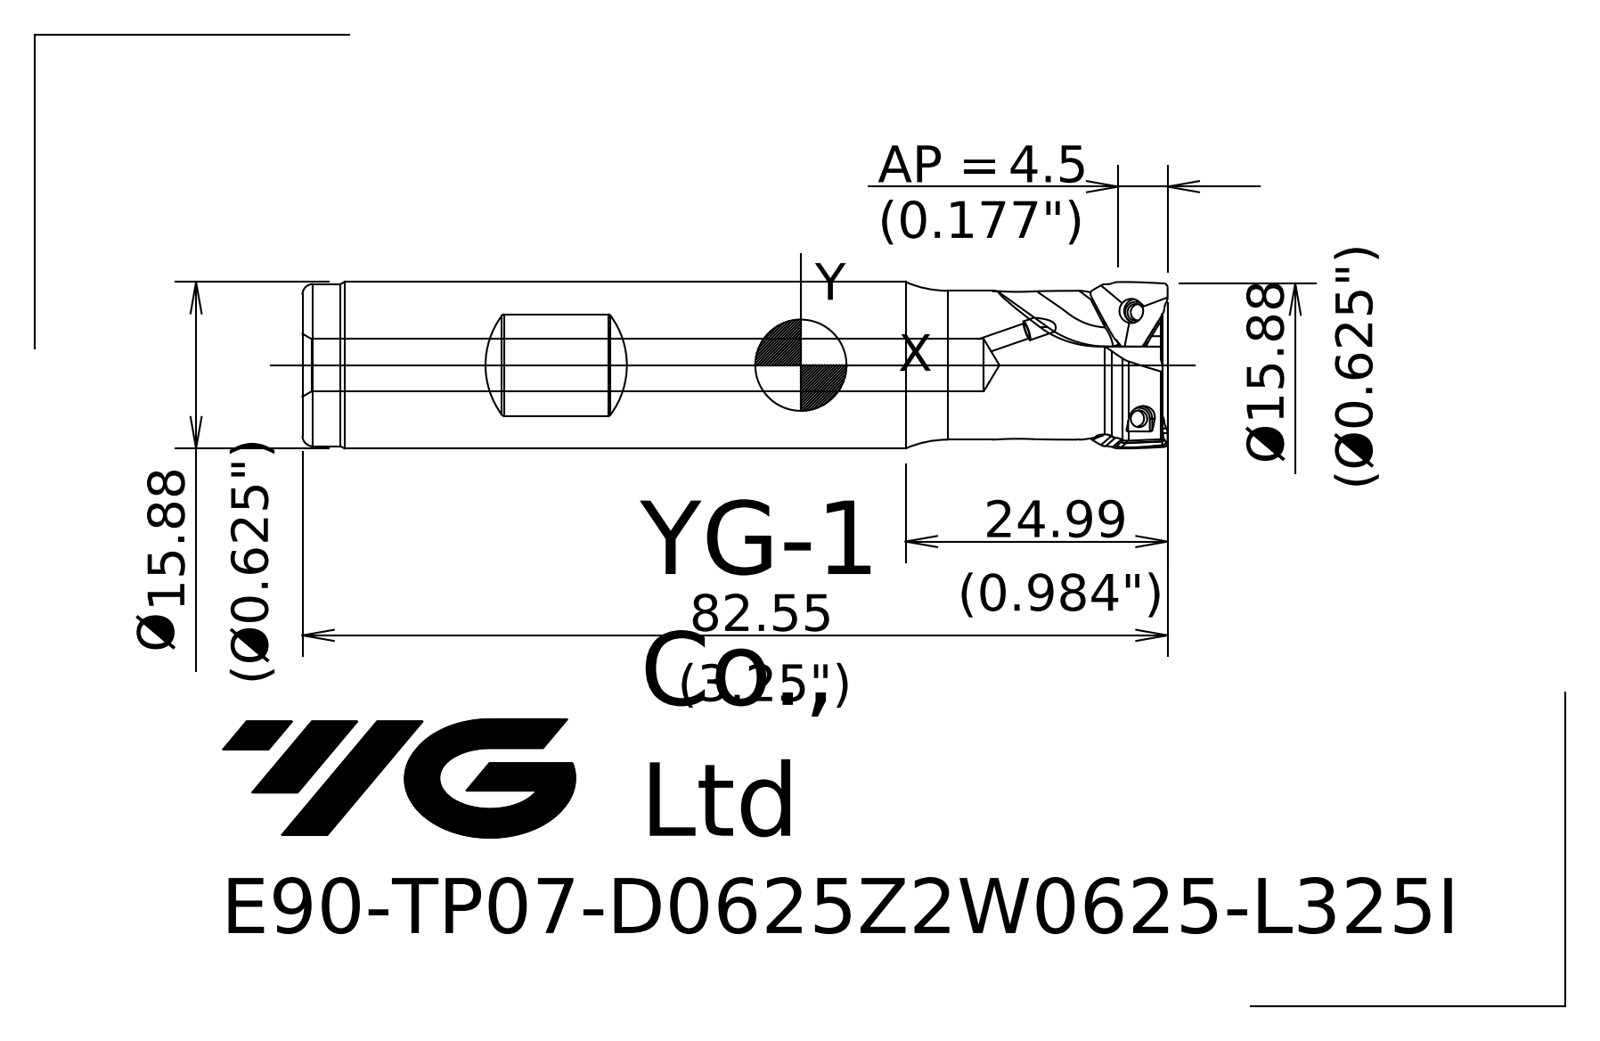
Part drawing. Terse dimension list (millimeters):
name: 102258EC0329yj36
written by: SIEMENS PLM Software NX 10.0 (AP203_CONFIGURATION_CONTROLLED_3D_DESIGN_OF_MECHANICAL_PARTS_AND_ASSEMBLIES_MIM_LF)
unit: mm
bodies: 1 solid, 45 faces (6 planar, 6 cylindrical, 33 other)
size: 82.55 × 15.91 × 15.91
volume: 13 891 mm³; area: 6 079 mm²
holes: 1× ⌀5
bosses: 1× ⌀15.88, 1× ⌀15.47, 1× ⌀14.2
rounds: 2× R0.3
face distances: 81.9, 82.05
